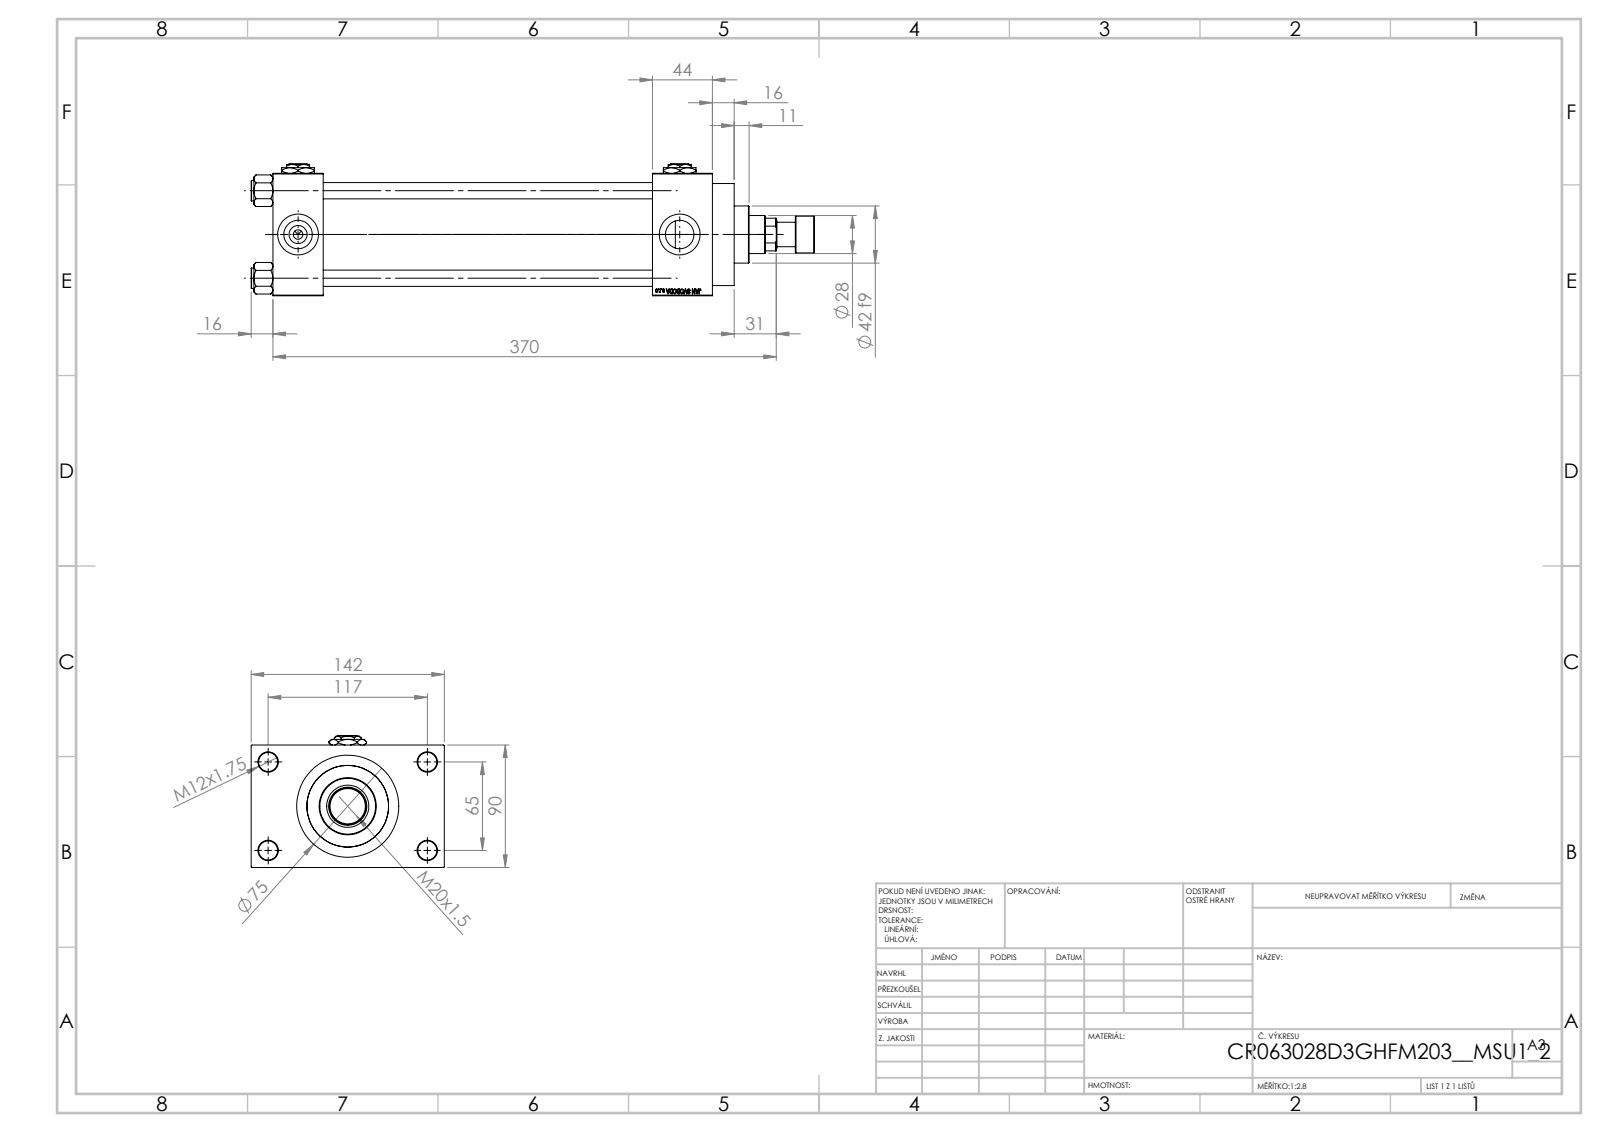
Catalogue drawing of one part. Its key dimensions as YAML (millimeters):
part_name: "V215CR_D_Body; Zatka_pro_OIL_PORT; V215CR_VCP_D; NUT_M5_D (+3 more)"
step_written_by: "SolidWorks 2019 (CONFIG_CONTROL_DESIGN)"
units: millimeters
bodies: {solids: 14, faces: 1218, planar: 549, cylindrical: 103, other: 566}
overall_size: [414, 142, 97]
volume: 1412000
surface_area: 327780
round_holes:
  - {diameter: 12, count: 4}
  - {diameter: 14, count: 4}
  - {diameter: 20.96, count: 4}
  - {diameter: 30, count: 4}
  - {diameter: 7, count: 3}
  - {diameter: 18.5, count: 1}
  - {diameter: 28, count: 1}
  - {diameter: 31, count: 1}
  - {diameter: 50, count: 1}
  - {diameter: 60, count: 1}
  - {diameter: 63, count: 1}
round_bosses_or_shafts:
  - {diameter: 15, count: 4}
  - {diameter: 75, count: 1}
  - {diameter: 69, count: 1}
  - {diameter: 42, count: 1}
  - {diameter: 27, count: 1}
  - {diameter: 18, count: 1}
face_to_face_distances: [90, 242, 37, 279, 286, 323, 44, 26, 116, 16]
hole_center_spacings: [26.35, 45.47, 64.3, 66.92, 69.81, 90.65, 111.34, 65]
